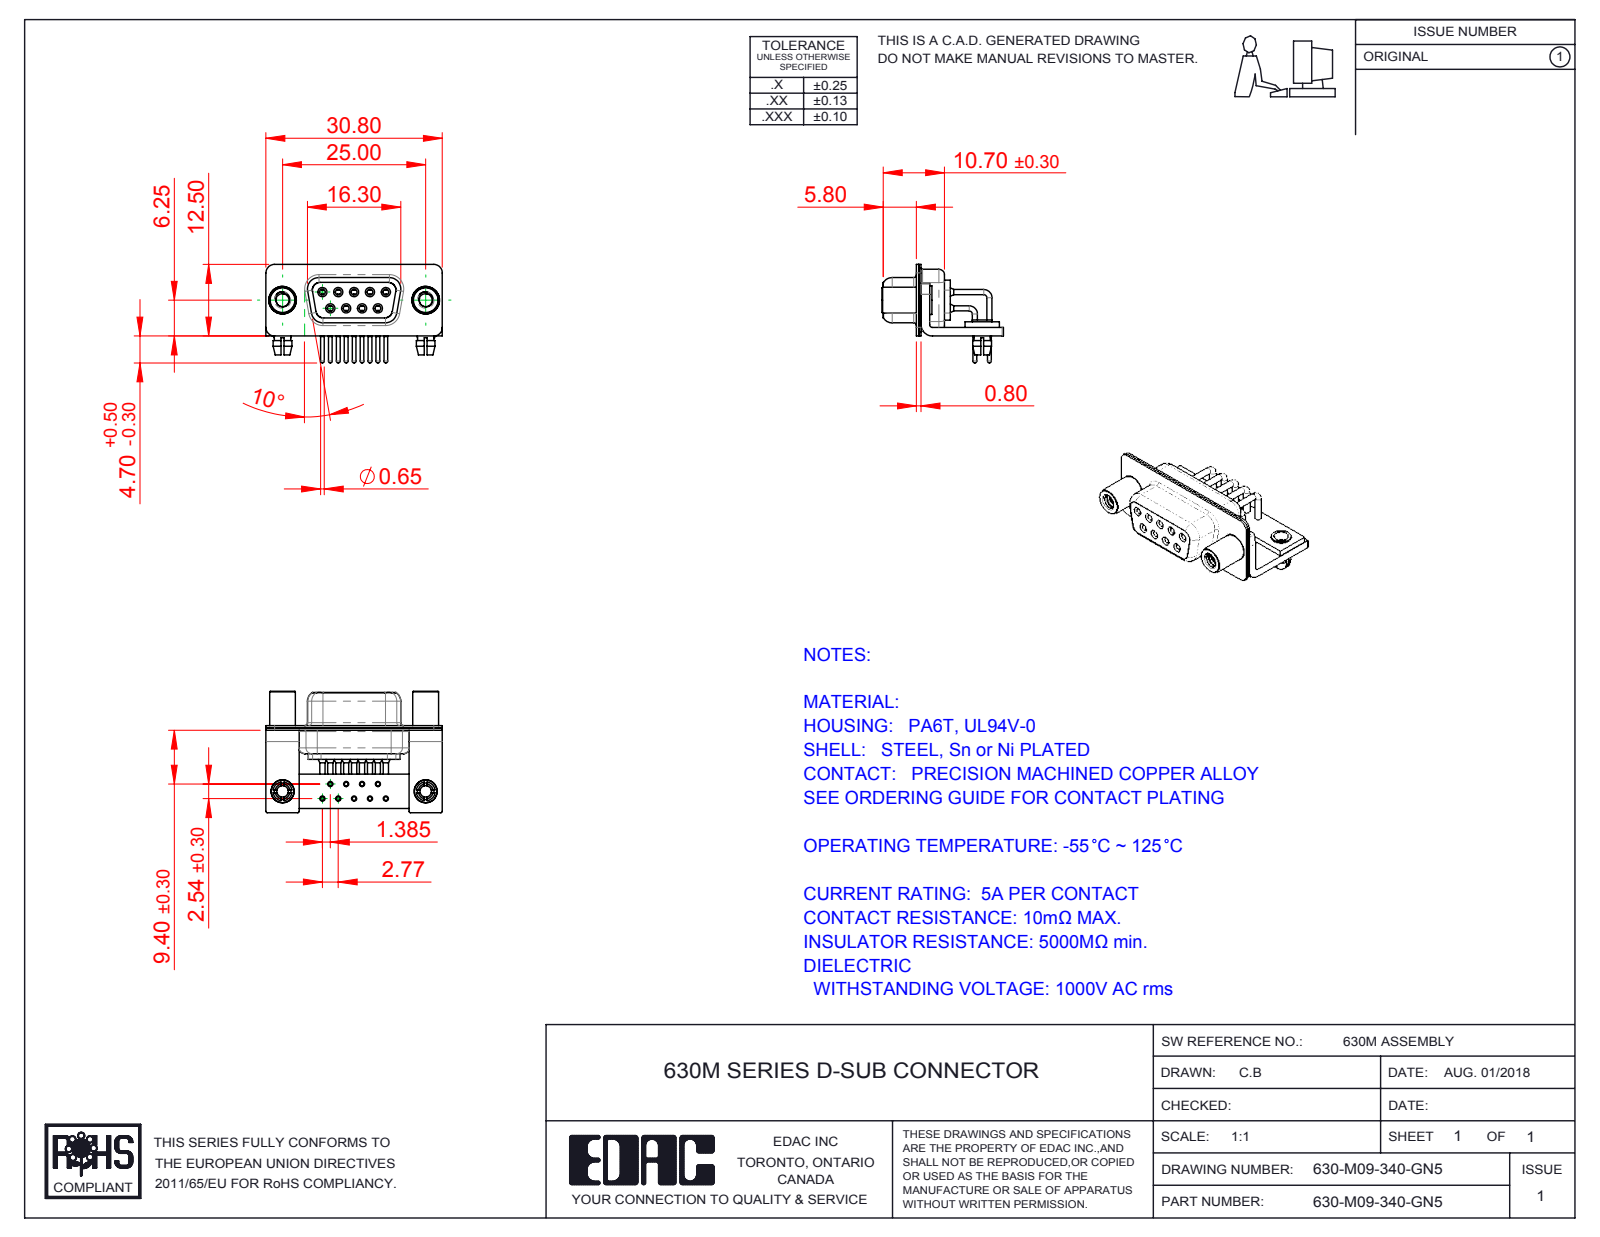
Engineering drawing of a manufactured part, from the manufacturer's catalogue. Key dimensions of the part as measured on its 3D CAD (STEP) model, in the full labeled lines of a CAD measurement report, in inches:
Part name (STEP PRODUCT): 630M Stabilizer Board_09 Contacts; 630M 4-40 Threaded Standoff; 630M Stabilizer Bracket; 630M Contact Row 2 (+6 more)
STEP written by: SolidWorks 2016 (CONFIG_CONTROL_DESIGN)
Units: inches
Bodies: 19 solids, 966 faces (278 planar, 458 cylindrical, 230 other)
Overall size (bounding box): 1.213 × 0.835 × 0.677
Volume: 0.144 in³ · Surface area: 9.669 in²
Round holes (diameter × count): ⌀0.079 ×11, ⌀0.035 ×9, ⌀0.039 ×9, ⌀0.043 ×9, ⌀0.067 ×9, ⌀0.071 ×9, ⌀0.089 ×2, ⌀0.098 ×2, ⌀0.126 ×2, ⌀0.157 ×2, ⌀0.189 ×2
Round bosses / shafts (diameter × count): ⌀0.063 ×9, ⌀0.059 ×9, ⌀0.035 ×9, ⌀0.026 ×9, ⌀0.197 ×2, ⌀0.193 ×2, ⌀0.177 ×2, ⌀0.157 ×2
Partial cylindrical surfaces — rounded edges, fillets, slot ends (radius × count): R0.01 ×16, R0.059 ×16, R0.079 ×13, R0.053 ×8, R0.063 ×8, R0.02 ×5, R0.024 ×4, R0.026 ×4
Main face-to-face distances: 0.016, 0.059, 0.031, 0.091, 0.075, 0.039, 0.368, 0.057, 0.335, 0.352
Hole centre spacings: 0.109, 0.218, 0.124, 0.192, 0.327, 0.114, 0.114, 0.198
